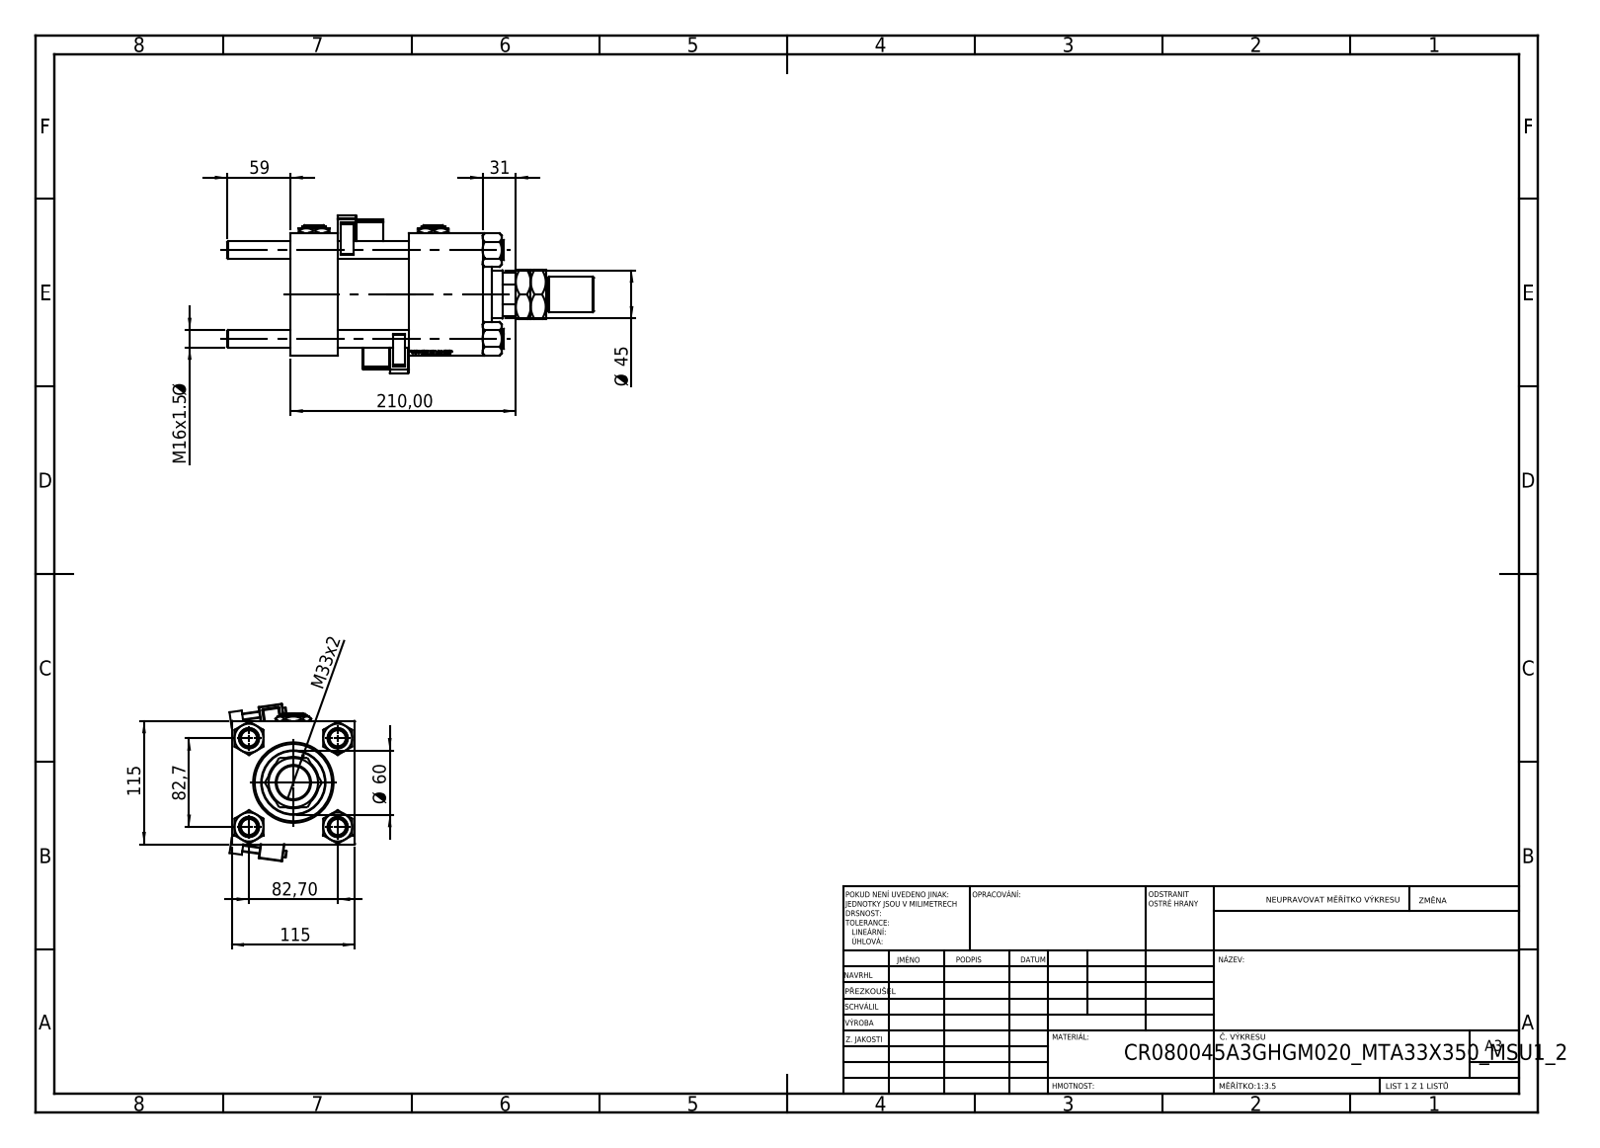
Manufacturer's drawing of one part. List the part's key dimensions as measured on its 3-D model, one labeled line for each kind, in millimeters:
Part name (STEP PRODUCT): V215CR_MSU; NUT_M5; V215CR_VCP; MTA (+4 more)
STEP written by: SolidWorks 2019 (CONFIG_CONTROL_DESIGN)
Units: millimetres
Bodies: 16 solids, 1484 faces (688 planar, 152 cylindrical, 644 other)
Overall size (bounding box): 342 × 146.66 × 117.01
Volume: 2 014 000 mm³ · Surface area: 332 066 mm²
Round holes (diameter × count): ⌀16 ×4, ⌀7 ×2, ⌀26.44 ×2, ⌀35 ×2, ⌀31.5 ×1, ⌀45 ×1, ⌀48 ×1, ⌀61 ×1, ⌀72 ×1, ⌀80 ×1
Round bosses / shafts (diameter × count): ⌀19 ×4, ⌀6 ×2, ⌀86 ×1, ⌀60 ×1, ⌀33 ×1, ⌀31 ×1
Partial cylindrical surfaces — rounded edges, fillets, slot ends (radius × count): R0.5 ×48, R1 ×2, R2.5 ×2, R4 ×2, R22 ×1
Main face-to-face distances: 115, 44, 179, 135, 110, 66, 69, 46, 20, 89
Hole centre spacings: 58.48, 82.7, 116.96, 111
